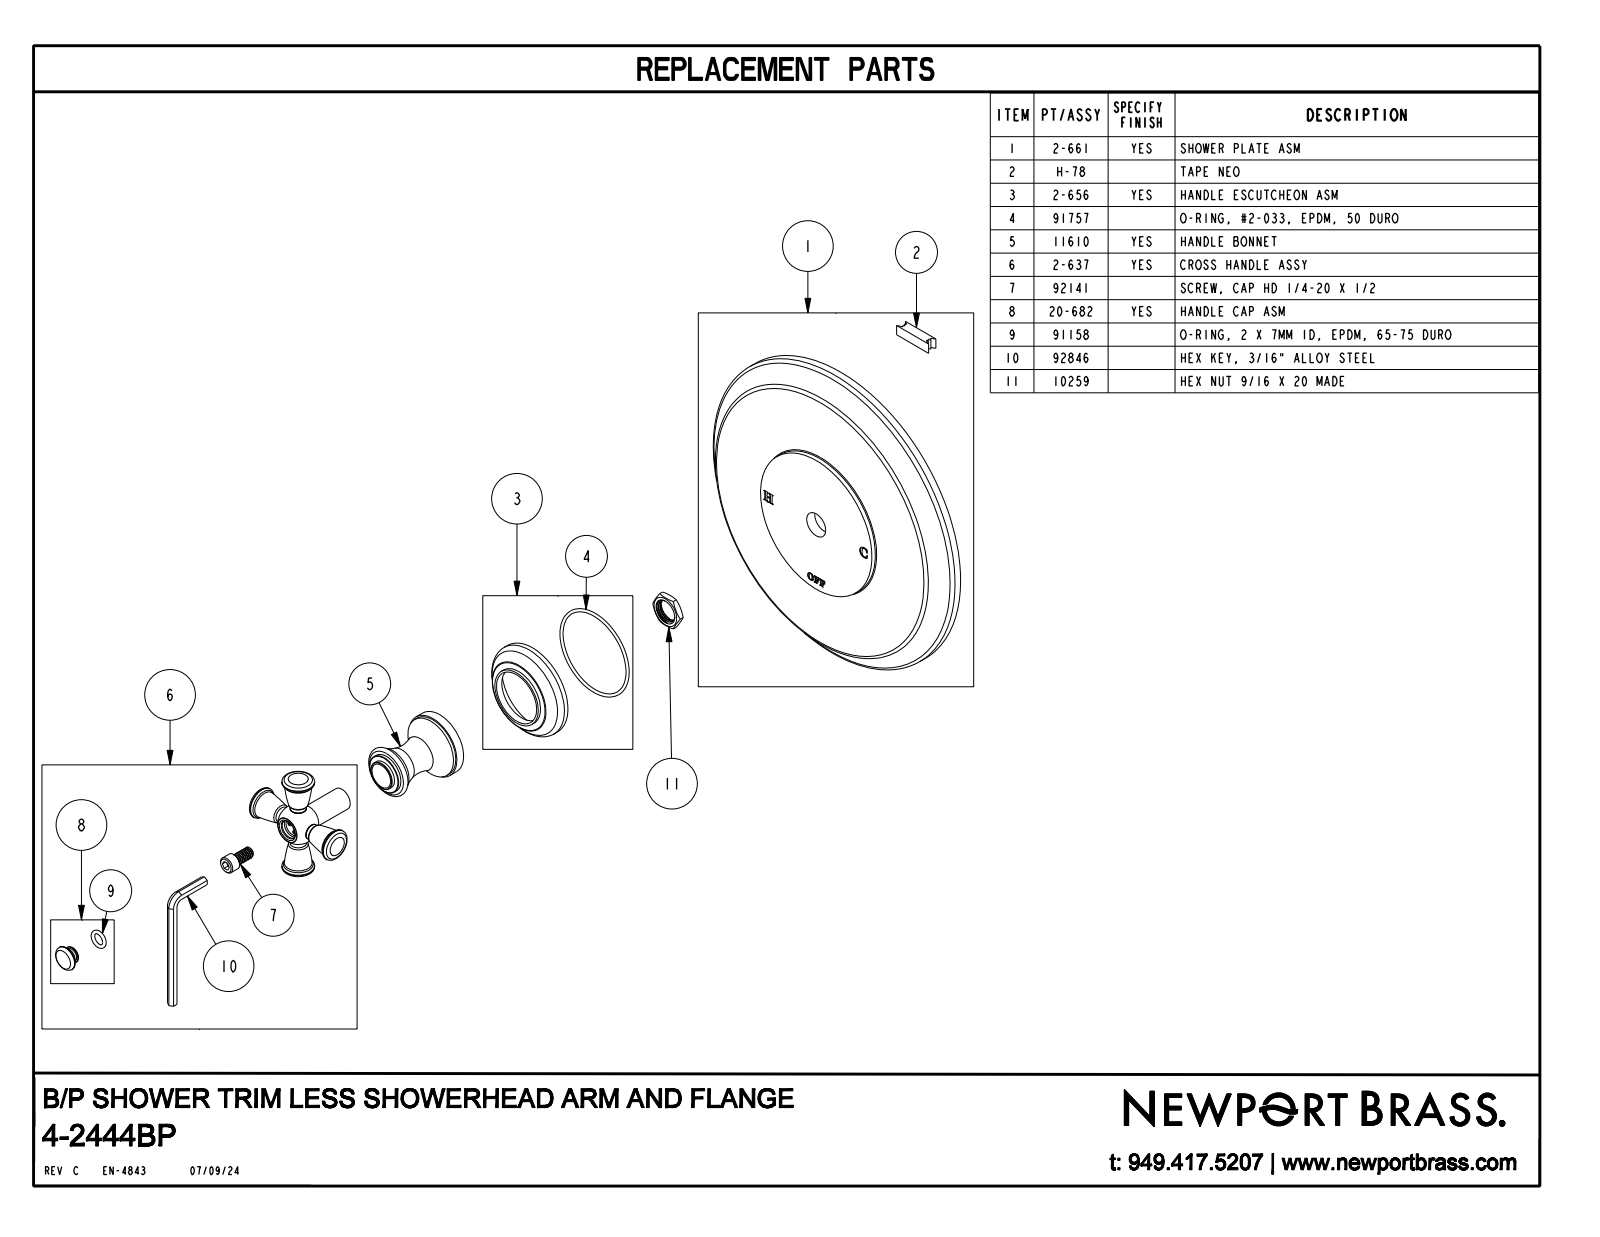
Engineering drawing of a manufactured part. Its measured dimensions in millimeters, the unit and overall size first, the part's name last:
Units: millimetres
Overall size (bounding box): 190.5 × 190.5 × 103.1
Round bosses / shafts (diameter × count): ⌀18.3 ×2, ⌀9.1 ×2, ⌀190.5 ×1, ⌀55.9 ×1, ⌀37.8 ×1, ⌀36.1 ×1, ⌀22.9 ×1, ⌀16.8 ×1
Main face-to-face distances: 15.9, 19.1, 3.2, 30, 14.1, 10.9, 2, 74.2, 58.3, 55.1
Volume: 489 200 mm³ · Surface area: 74 320 mm²
Bodies: 1 solid, 273 faces (42 planar, 32 cylindrical, 199 other)
Part name (STEP PRODUCT): 4-2444BP
STEP written by: CREO PARAMETRIC BY PTC INC, 2018400 (CONFIG_CONTROL_DESIGN)
